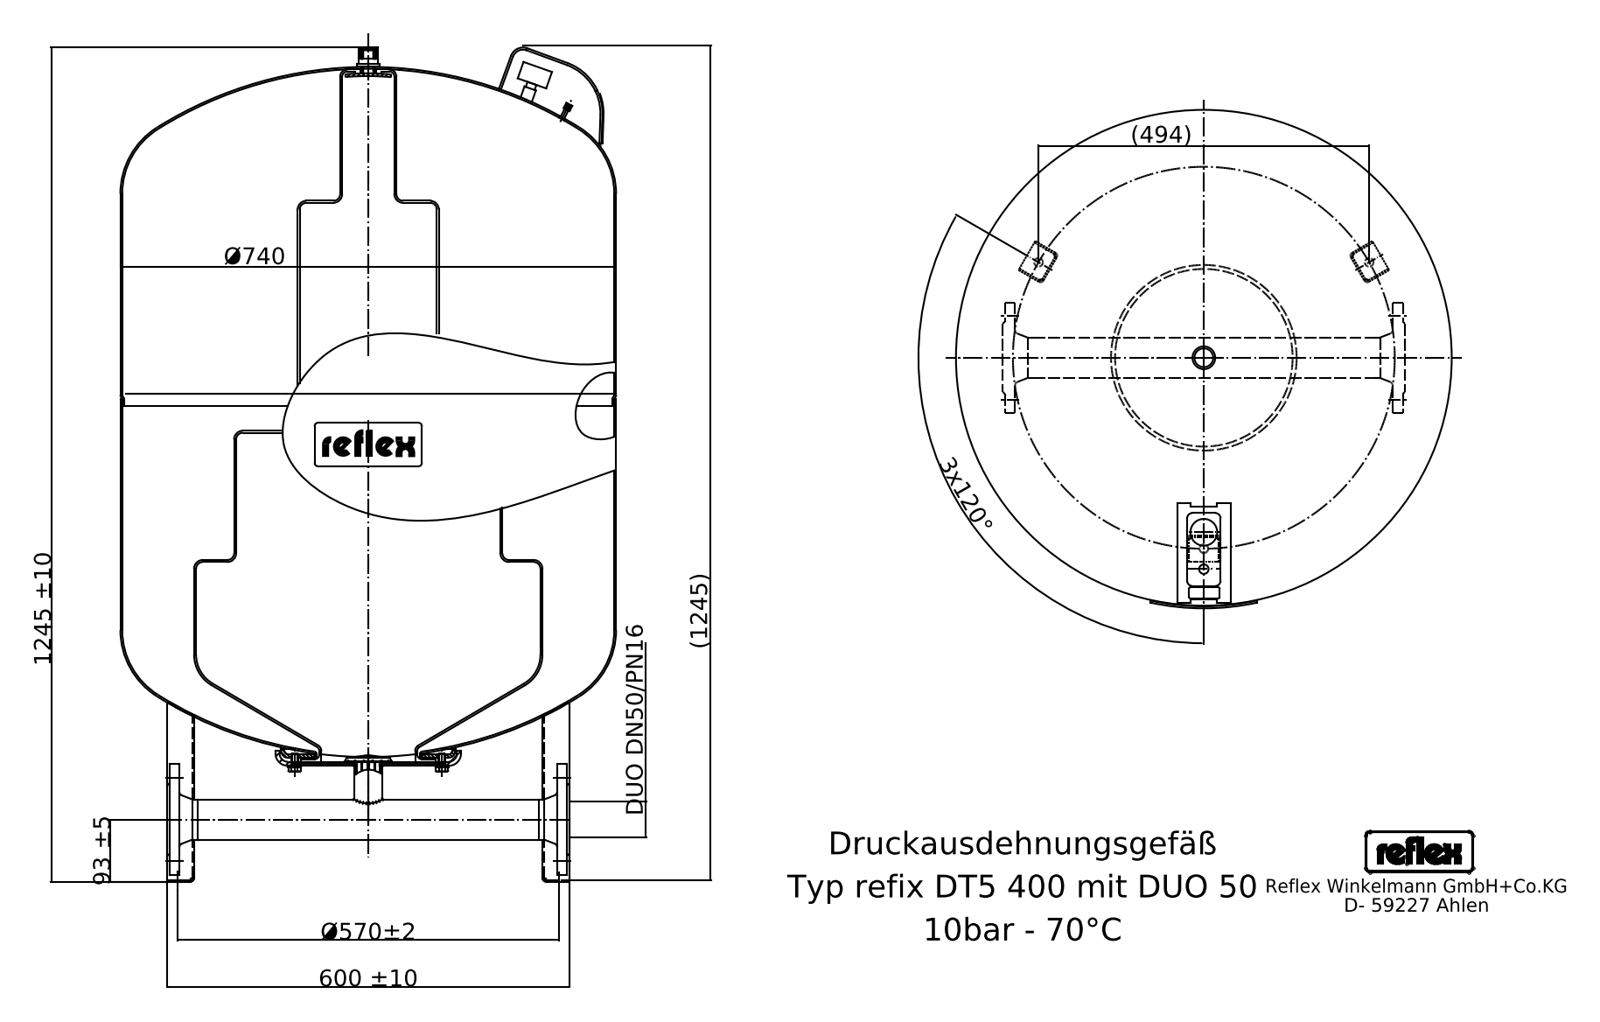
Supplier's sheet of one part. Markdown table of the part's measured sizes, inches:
| quantity | value |
| --- | --- |
| STEP written by | Mechanical Desktop 2008 (CONFIG_CONTROL_DESIGN) |
| units | inches |
| bodies | 23 solids, 513 faces (225 planar, 180 cylindrical, 108 other) |
| overall size | 49.016 × 29.134 × 29.134 |
| volume | 23 820 in³ |
| surface area | 7 983 in² |
| round holes (diameter × count) | 0.748 × 4, 0.528 × 3, 0.098 × 1, 0.276 × 1, 0.315 × 1, 0.449 × 1, 2.374 × 1, 6.181 × 1, 9.843 × 1 |
| round bosses / shafts (diameter × count) | 0.394 × 9, 29.134 × 1, 10.236 × 1, 9.055 × 1, 6.496 × 1, 2.441 × 1, 1.669 × 1, 1.339 × 1 |
| partial cylindrical surfaces (radius × count) | 0.039 × 15, 0.098 × 15, 0.197 × 15, 0.221 × 4, 0.089 × 3, 0.151 × 2, 0.266 × 2, 0.315 × 2 |
| main face-to-face distances | 25.669, 0.098, 1.87, 7.717, 33.386, 0.236, 7.953, 33.622, 1.969, 1.772 |
| hole center spacings | 2.46, 3.48, 11.22, 19.435, 4.921 |
